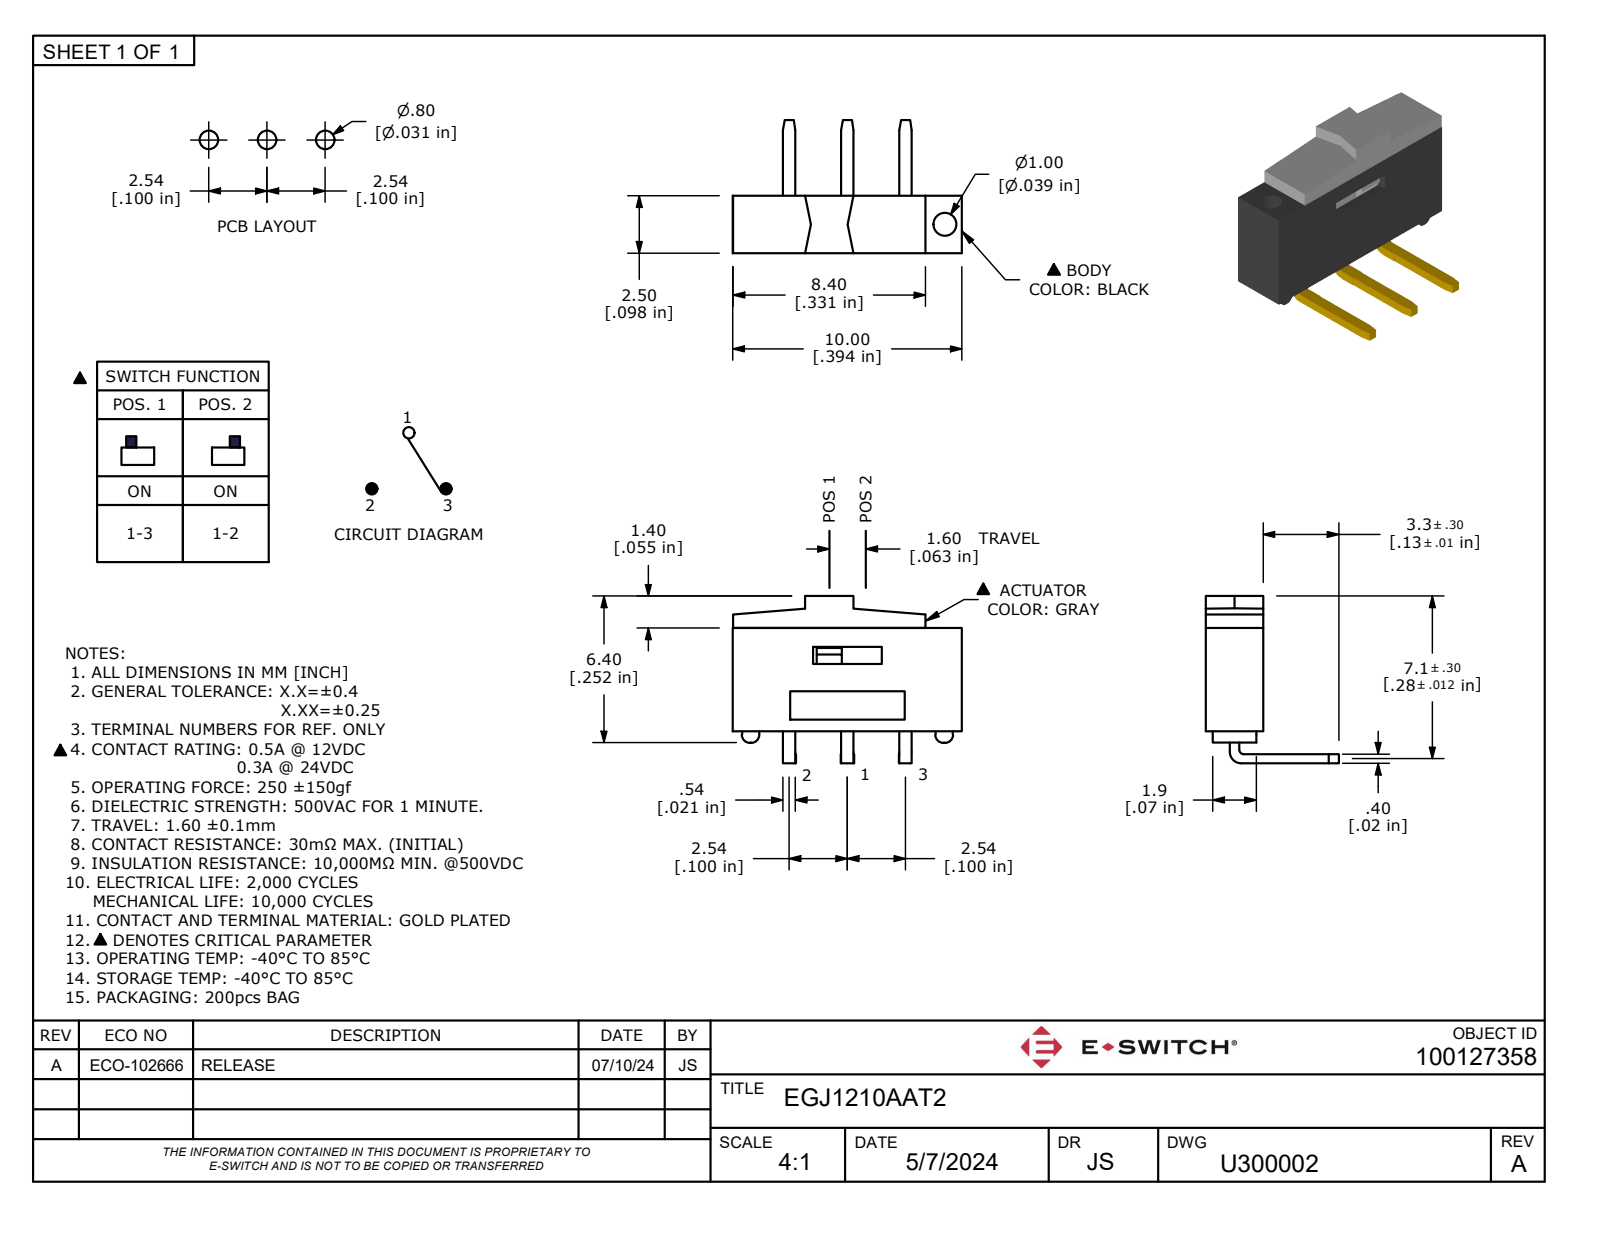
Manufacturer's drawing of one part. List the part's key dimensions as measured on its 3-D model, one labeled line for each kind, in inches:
Part name (STEP PRODUCT): EGJ1210AAT2
STEP written by: Autodesk Inventor 2022 (AUTOMOTIVE_DESIGN)
Units: inches
Bodies: 1 solid, 117 faces (106 planar, 11 cylindrical, 0 other)
Overall size (bounding box): 0.394 × 0.287 × 0.229
Volume: 0.006 in³ · Surface area: 0.529 in²
Round holes (diameter × count): ⌀0.039 ×1
Partial cylindrical surfaces — rounded edges, fillets, slot ends (radius × count): R0.014 ×4, R0.008 ×1, R0.02 ×1
Main face-to-face distances: 0.017, 0.081, 0.098, 0.02, 0.065, 0.062, 0.079, 0.016, 0.067, 0.059
